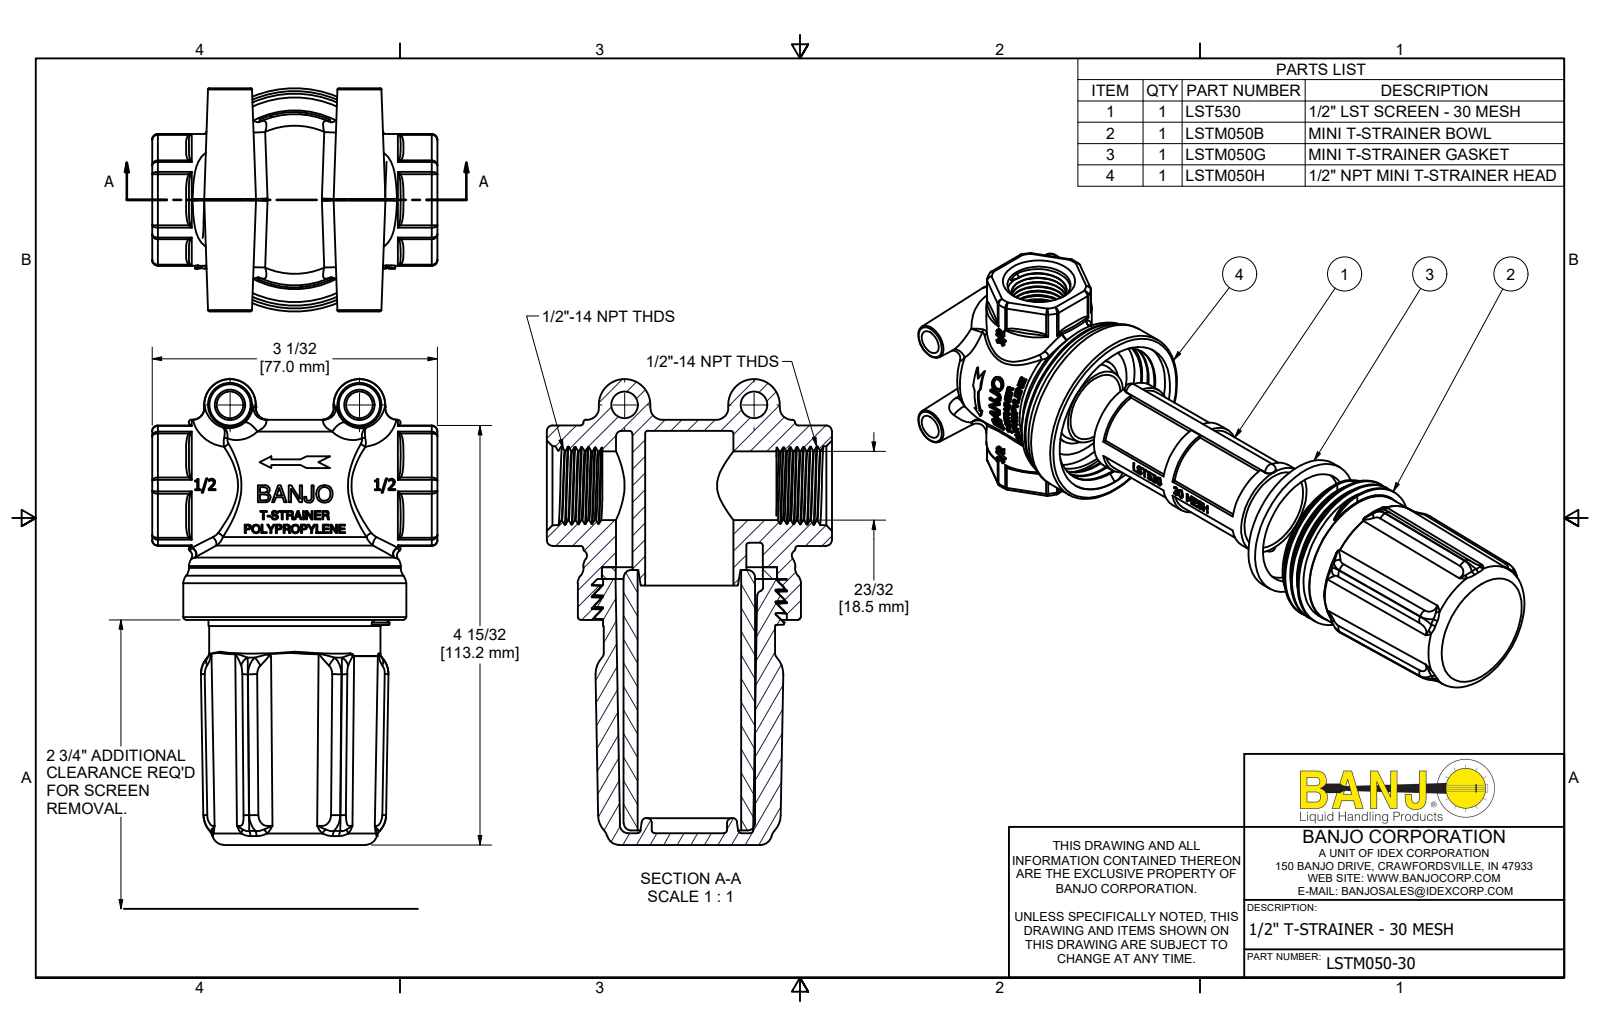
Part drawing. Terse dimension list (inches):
name: LSTM050-30; LSTM050H; LSTM050G; LST530 (+1 more)
written by: Autodesk Inventor 2019 (AUTOMOTIVE_DESIGN)
unit: in
bodies: 4 solids, 1389 faces (560 planar, 190 cylindrical, 639 other)
size: 24.12 × 4.947 × 2.37
volume: 8.173 in³; area: 190.8 in²
holes: 1× ⌀0.73, 1× ⌀0.8, 1× ⌀0.937, 1× ⌀1.101, 1× ⌀1.56, 1× ⌀1.563, 1× ⌀1.891, 1× ⌀2.073
bosses: 1× ⌀2.37, 1× ⌀2.25, 1× ⌀2.01, 1× ⌀1.861, 1× ⌀1.86, 1× ⌀1.833, 1× ⌀1.82, 1× ⌀1.4
rounds: 24× R0.06, 4× R0.03, 4× R0.08, 3× R0.05, 2× R0.084, 1× R0.26, 1× R0.55, 1× R0.576
face distances: 2.825, 2.95, 0.125, 1.28, 4.515, 1.69, 1.565, 4.397, 1.572, 1.447
